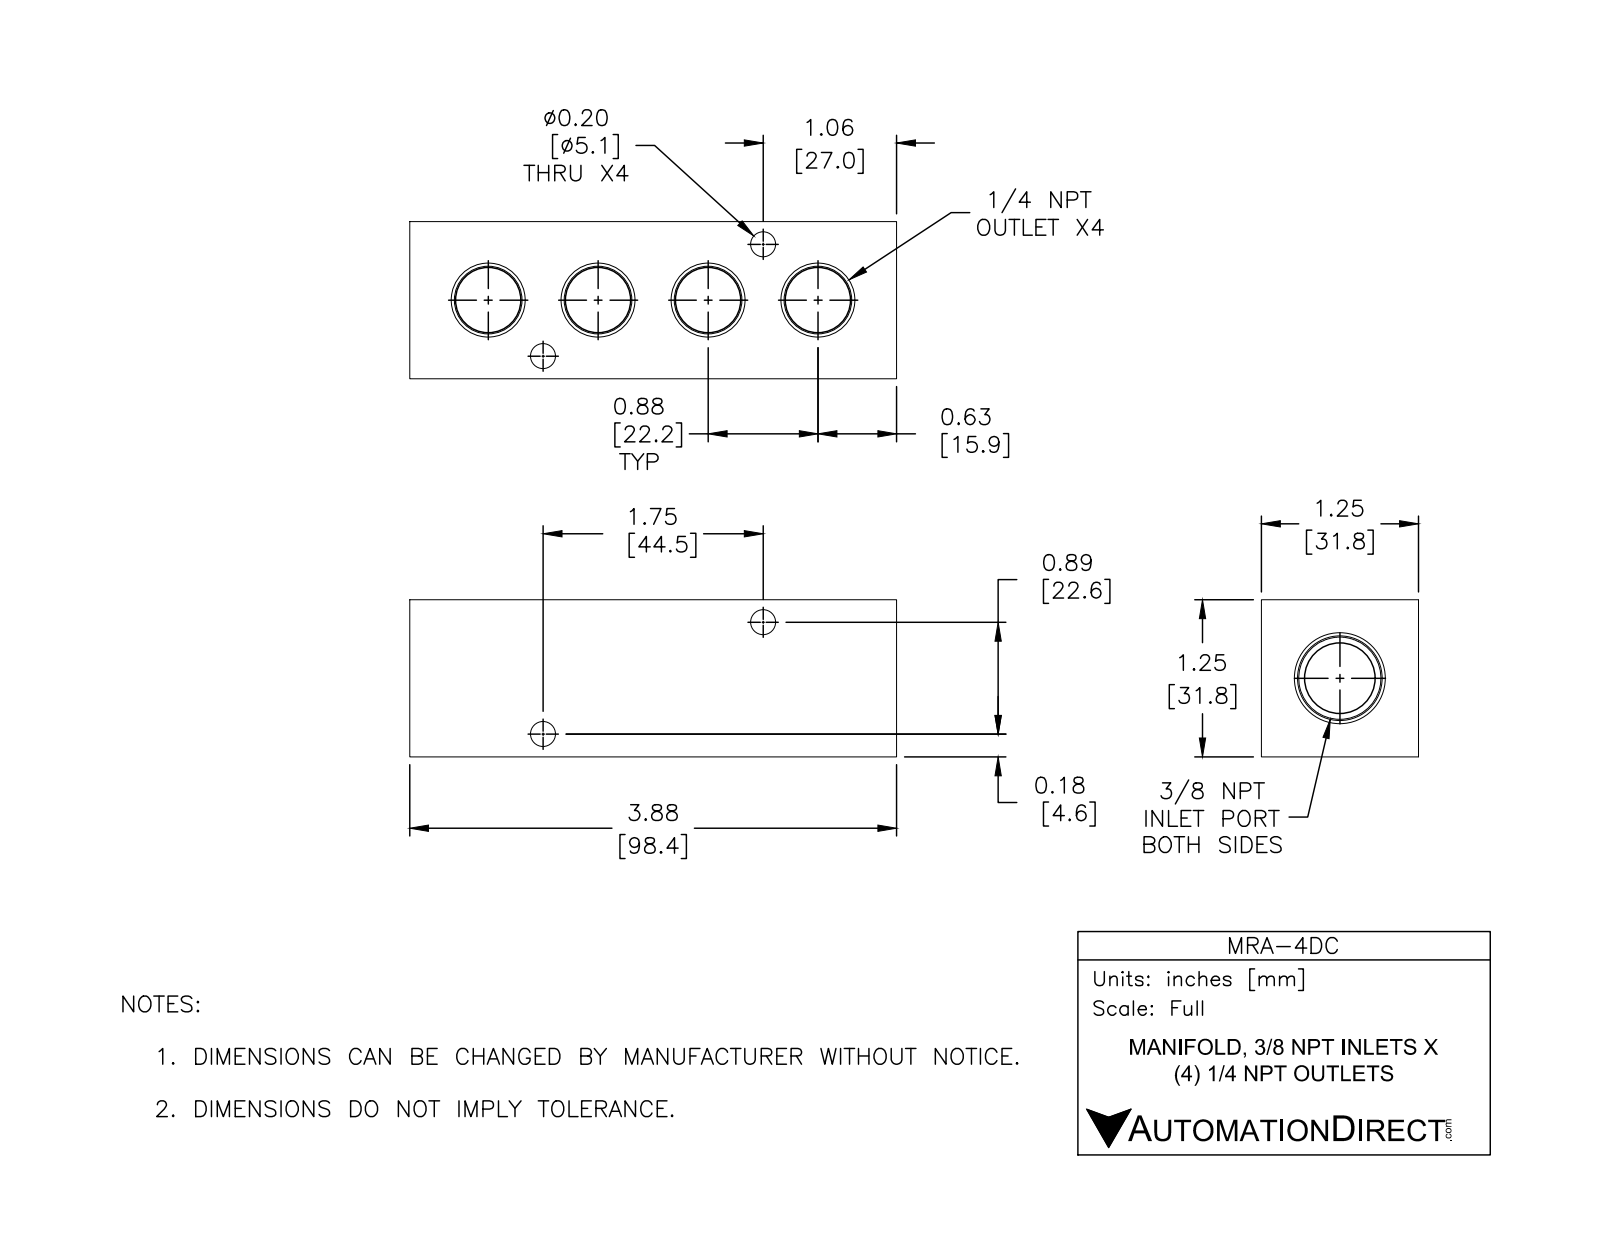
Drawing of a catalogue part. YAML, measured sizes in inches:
part_name: "MRA-4DC"
step_written_by: "SolidWorks 2015 (CONFIG_CONTROL_DESIGN)"
units: inches
bodies: {solids: 1, faces: 66, planar: 16, cylindrical: 26, other: 24}
overall_size: [3.875, 1.25, 1.25]
volume: 4.537
surface_area: 32.47
round_holes:
  - {diameter: 0.2, count: 4}
  - {diameter: 0.562, count: 1}
partial_cylinders:
  - {radius: 0.219, count: 4}
face_to_face_distances: [1.25, 3.875, 0.41, 3.465, 0.86, 0.39, 3.055]
hole_center_spacings: [1.963]
